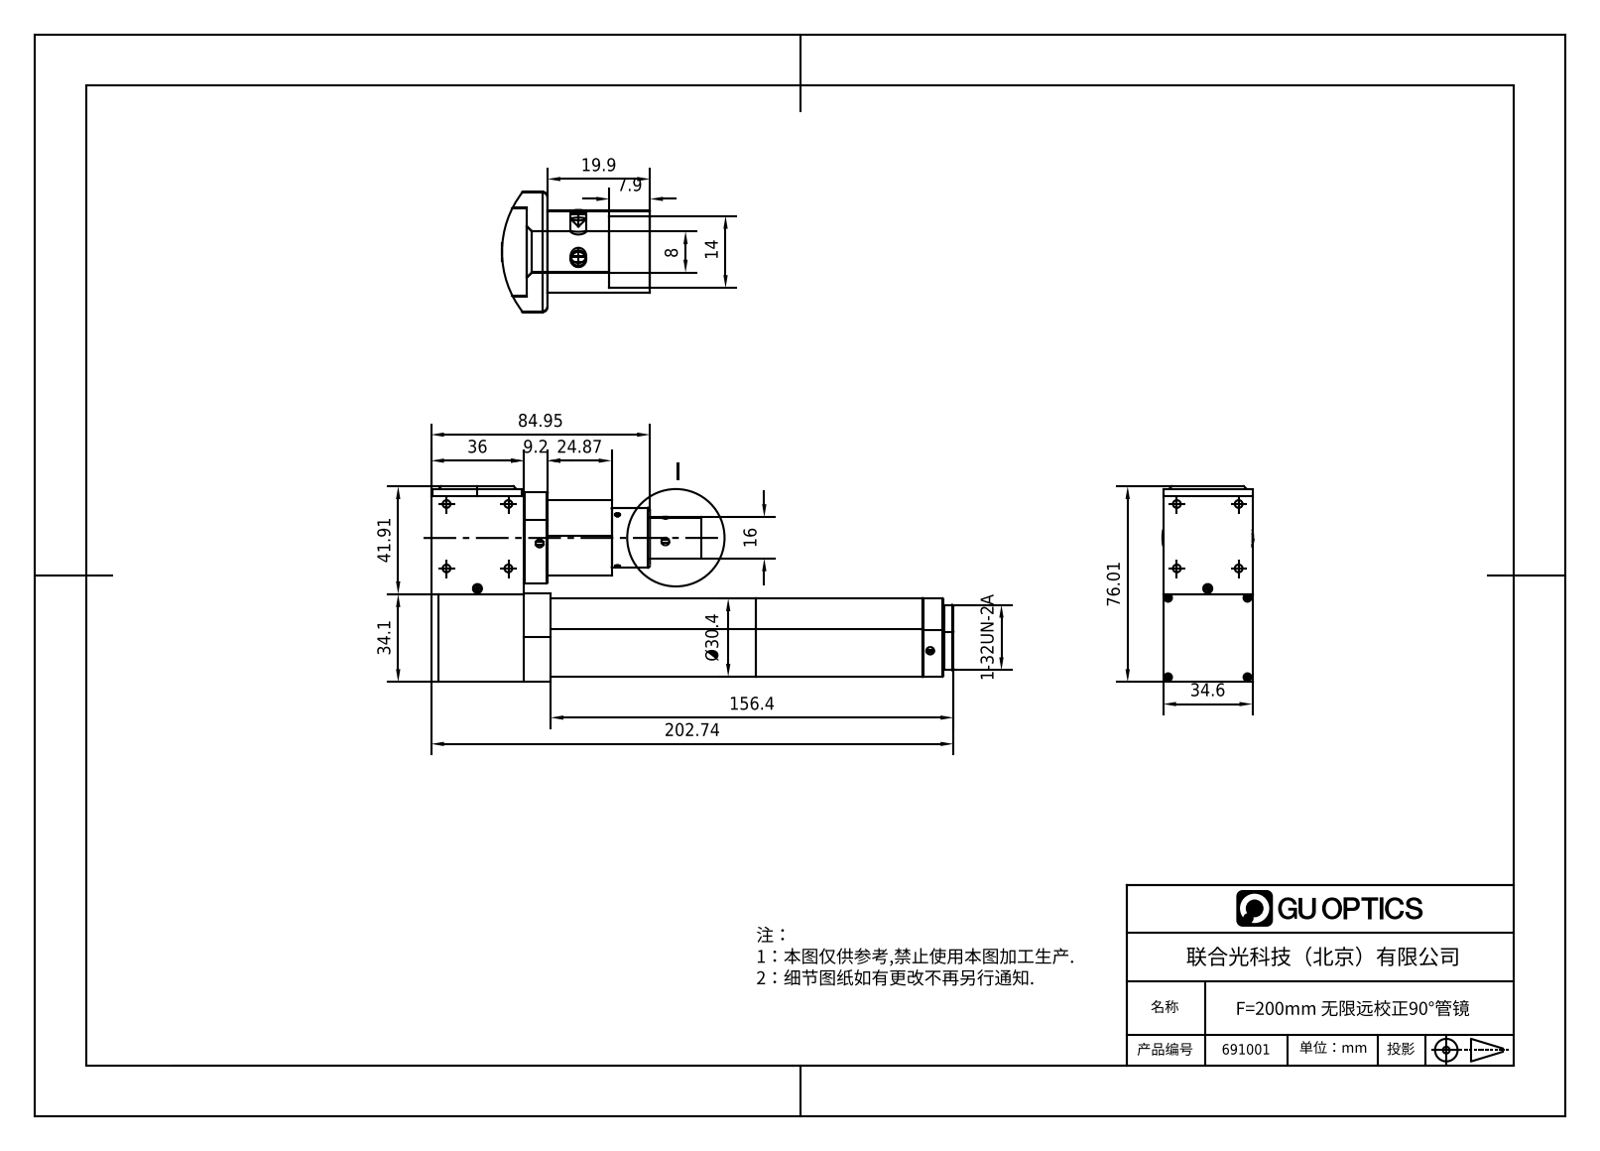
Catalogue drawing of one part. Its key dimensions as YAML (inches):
part_name: "PLC029A063.STEP; 90度管镜外观图 T2022-02-25; M2X3尖端螺钉.STEP; PLC029A010.STEP (+8 more)"
step_written_by: "SolidWorks 2020 (CONFIG_CONTROL_DESIGN)"
units: inches
bodies: {solids: 32, faces: 701, planar: 351, cylindrical: 258, other: 92}
overall_size: [7.986, 2.993, 1.391]
volume: 14.9
surface_area: 94.68
round_holes:
  - {diameter: 0.118, count: 18}
  - {diameter: 0.079, count: 12}
  - {diameter: 0.063, count: 4}
  - {diameter: 0.138, count: 2}
  - {diameter: 0.13, count: 1}
  - {diameter: 0.315, count: 1}
  - {diameter: 0.551, count: 1}
  - {diameter: 0.673, count: 1}
  - {diameter: 0.677, count: 1}
  - {diameter: 0.803, count: 1}
  - {diameter: 0.819, count: 1}
  - {diameter: 0.843, count: 1}
round_bosses_or_shafts:
  - {diameter: 0.098, count: 8}
  - {diameter: 0.118, count: 5}
  - {diameter: 0.063, count: 4}
  - {diameter: 1.362, count: 2}
  - {diameter: 0.11, count: 2}
  - {diameter: 0.079, count: 2}
  - {diameter: 1.386, count: 1}
  - {diameter: 1.197, count: 1}
partial_cylinders:
  - {radius: 0.008, count: 4}
  - {radius: 0.039, count: 4}
  - {radius: 0.004, count: 2}
  - {radius: 0.059, count: 2}
face_to_face_distances: [0.017, 0.118, 1.362, 1.295, 1.417, 1.343, 0.122, 1.38, 1.345, 1.413]
hole_center_spacings: [0.563, 0.621, 0.857, 0.945, 0.984, 1.213, 1.365, 1.375]
